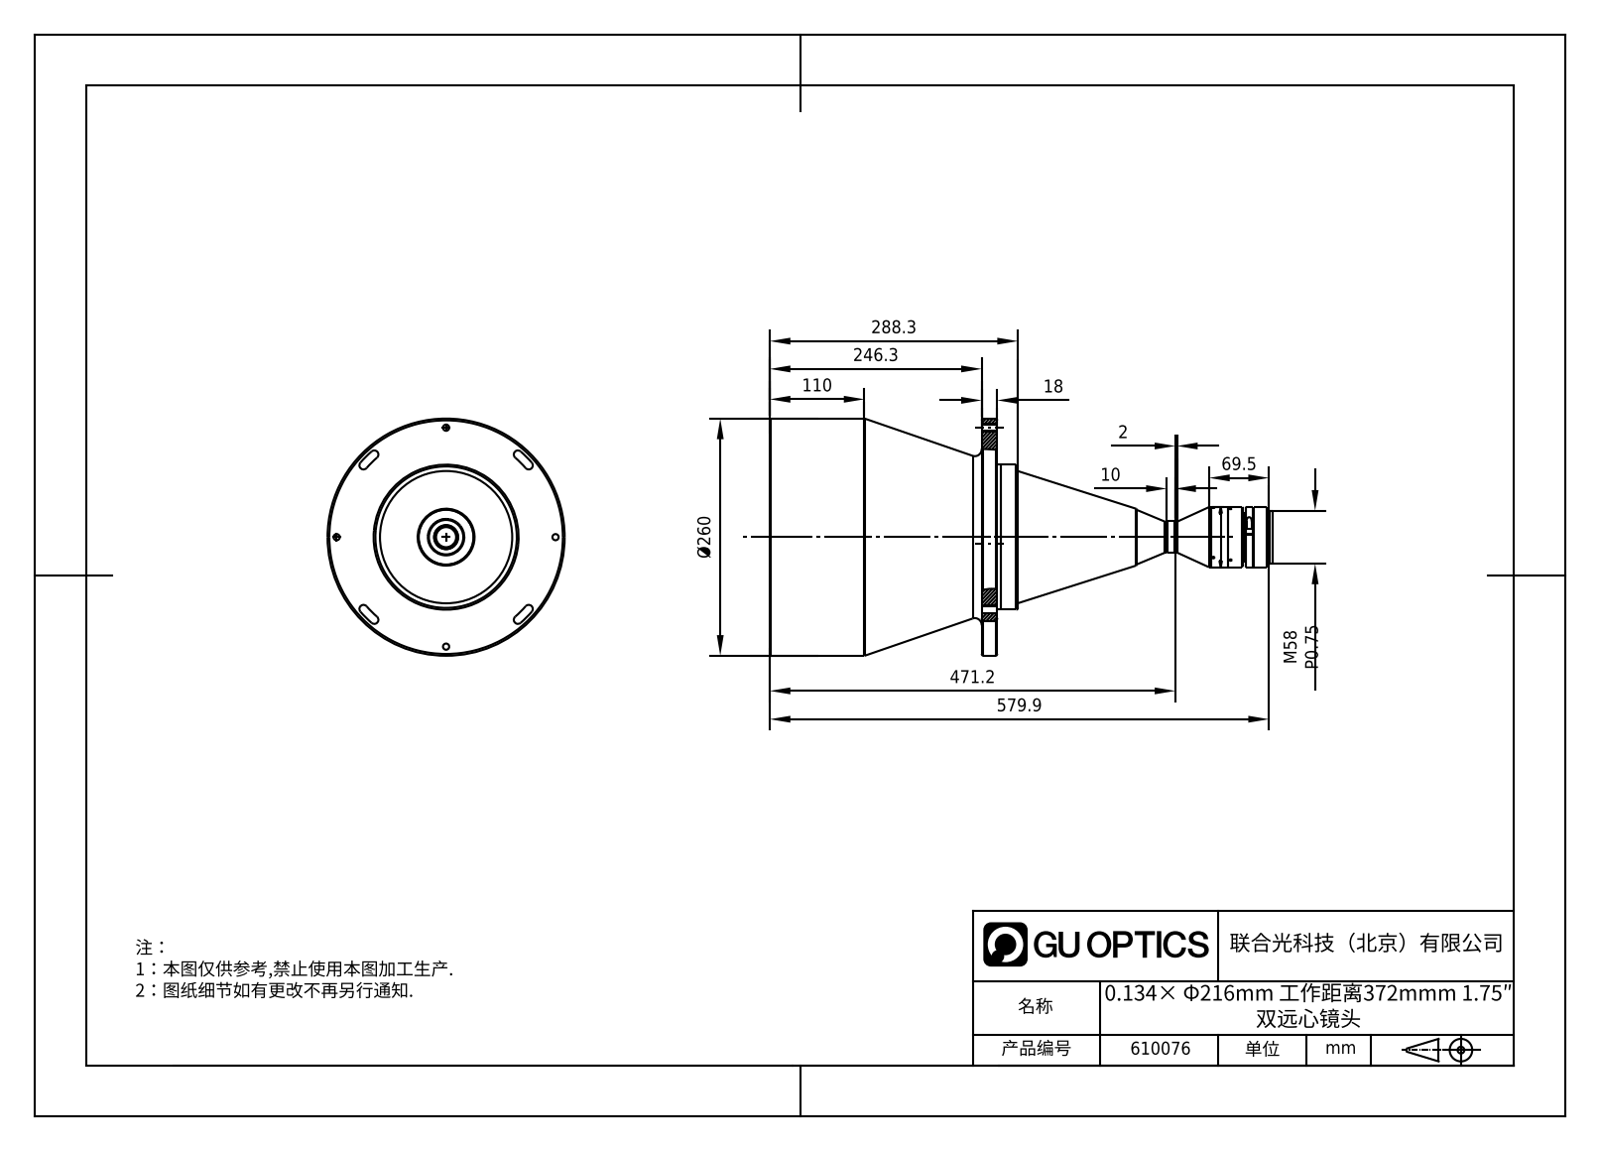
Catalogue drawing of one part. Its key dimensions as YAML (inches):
part_name: "DTCM175-216-M58-AL"
step_written_by: "SolidWorks 2017 (CONFIG_CONTROL_DESIGN)"
units: inches
bodies: {solids: 1, faces: 123, planar: 11, cylindrical: 66, other: 46}
overall_size: [23.008, 10.236, 10.236]
volume: 849.5
surface_area: 641.7
round_holes:
  - {diameter: 0.098, count: 6}
  - {diameter: 0.268, count: 4}
round_bosses_or_shafts:
  - {diameter: 10.236, count: 1}
  - {diameter: 6.26, count: 1}
  - {diameter: 2.598, count: 1}
  - {diameter: 2.323, count: 1}
  - {diameter: 2.283, count: 1}
  - {diameter: 2.205, count: 1}
  - {diameter: 1.378, count: 1}
  - {diameter: 1.339, count: 1}
partial_cylinders:
  - {radius: 0.177, count: 8}
  - {radius: 4.547, count: 1}
  - {radius: 4.902, count: 1}
face_to_face_distances: [10.406, 9.697, 0.709, 23.008, 13.311, 12.602, 11.35, 1.654, 0.945, 11.657]
hole_center_spacings: [6.681, 9.449]
